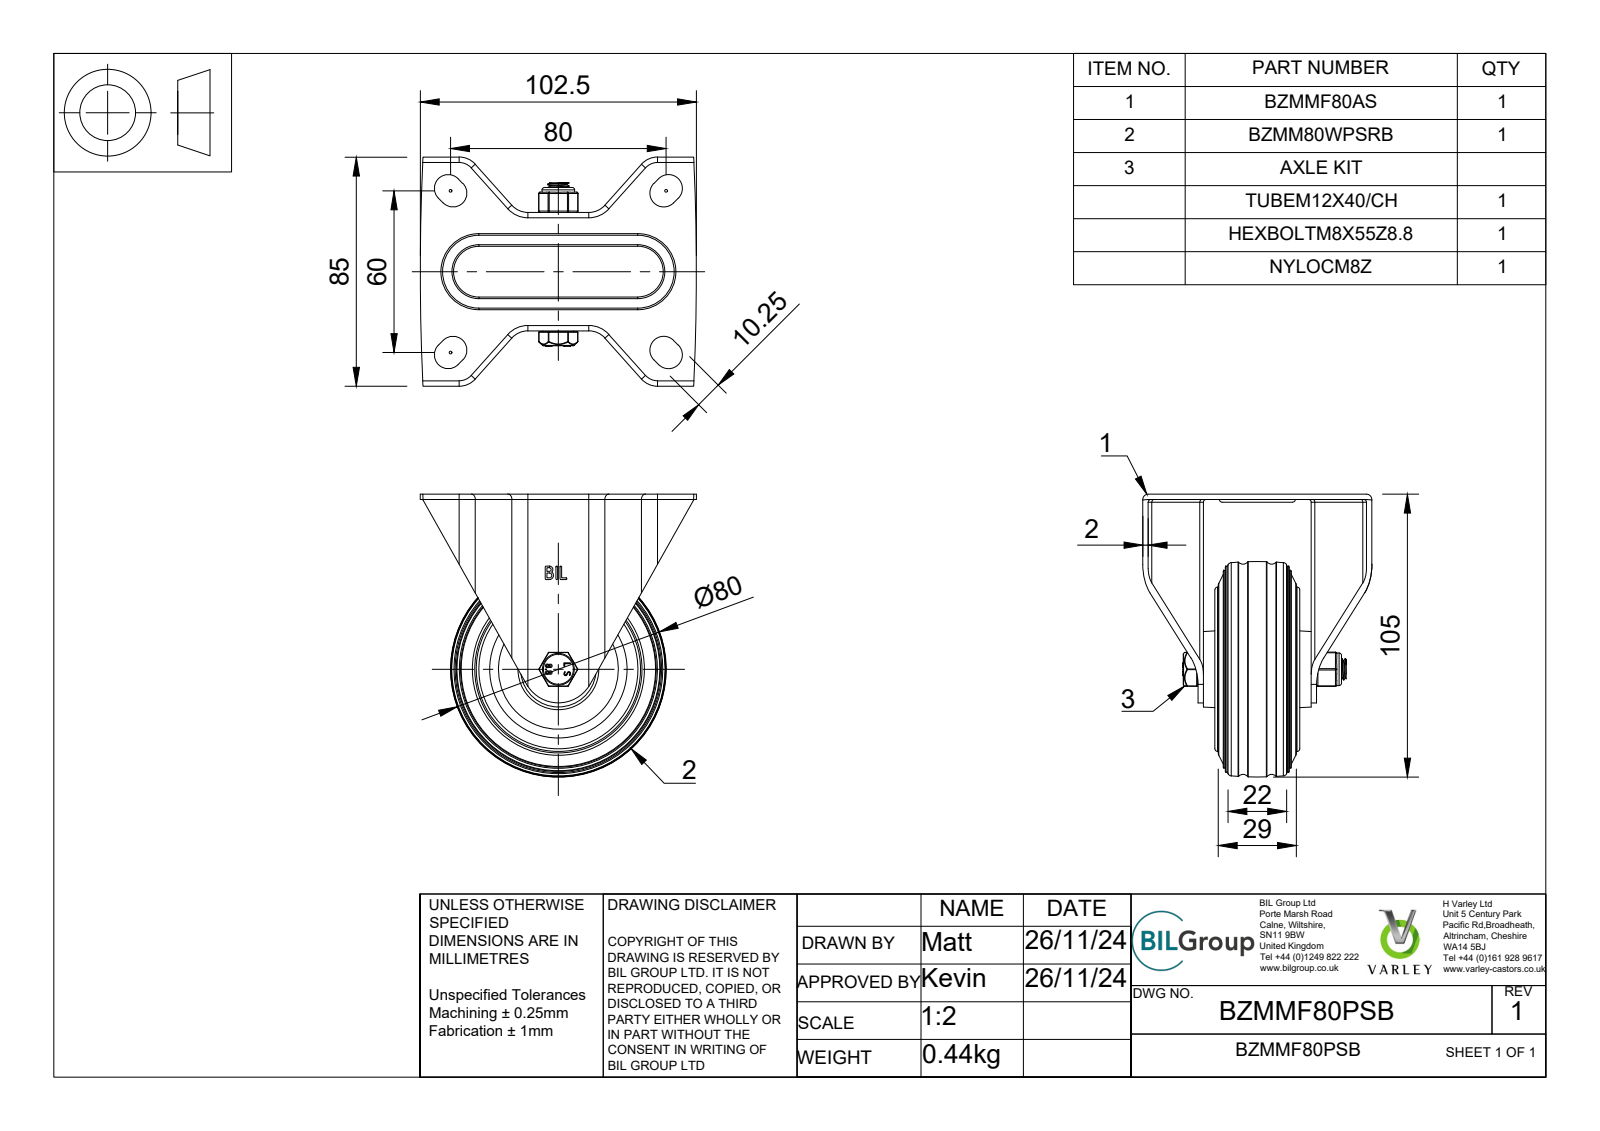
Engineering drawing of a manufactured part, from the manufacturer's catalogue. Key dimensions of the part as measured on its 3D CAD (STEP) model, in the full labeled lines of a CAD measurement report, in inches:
Part name (STEP PRODUCT): BZMMF80PSB v3; BZMMF80AS - 40 v2; ZINC PLATED, PRESSED STEEL BRACKET (1); BZMM80WPSRB v1 (+7 more)
STEP written by: Autodesk Translation Framework v13.20.0.188 (AP242_MANAGED_MODEL_BASED_3D_ENGINEERING_MIM_LF)
Units: inches
Bodies: 17 solids, 528 faces (198 planar, 198 cylindrical, 132 other)
Overall size (bounding box): 4.134 × 4.035 × 3.346
Volume: 9.22 in³ · Surface area: 132.3 in²
Round holes (diameter × count): ⌀0.026 ×2, ⌀0.315 ×1, ⌀0.325 ×1, ⌀0.331 ×1, ⌀0.339 ×1, ⌀0.48 ×1, ⌀0.492 ×1, ⌀0.787 ×1, ⌀0.984 ×1, ⌀1.902 ×1, ⌀2.008 ×1, ⌀2.165 ×1
Round bosses / shafts (diameter × count): ⌀0.148 ×8, ⌀2.402 ×1, ⌀0.98 ×1, ⌀0.768 ×1, ⌀0.476 ×1, ⌀0.469 ×1, ⌀0.453 ×1, ⌀0.31 ×1
Partial cylindrical surfaces — rounded edges, fillets, slot ends (radius × count): R0.02 ×18, R0.01 ×12, R0.039 ×12, R0.315 ×9, R0.079 ×8, R0.157 ×8, R0.202 ×8, R0.013 ×4
Main face-to-face distances: 0.079, 0.203, 1.654, 0.679, 0.217, 0.295, 0.974, 1.575, 1.437, 1.358
Hole centre spacings: 0.127, 0.098
